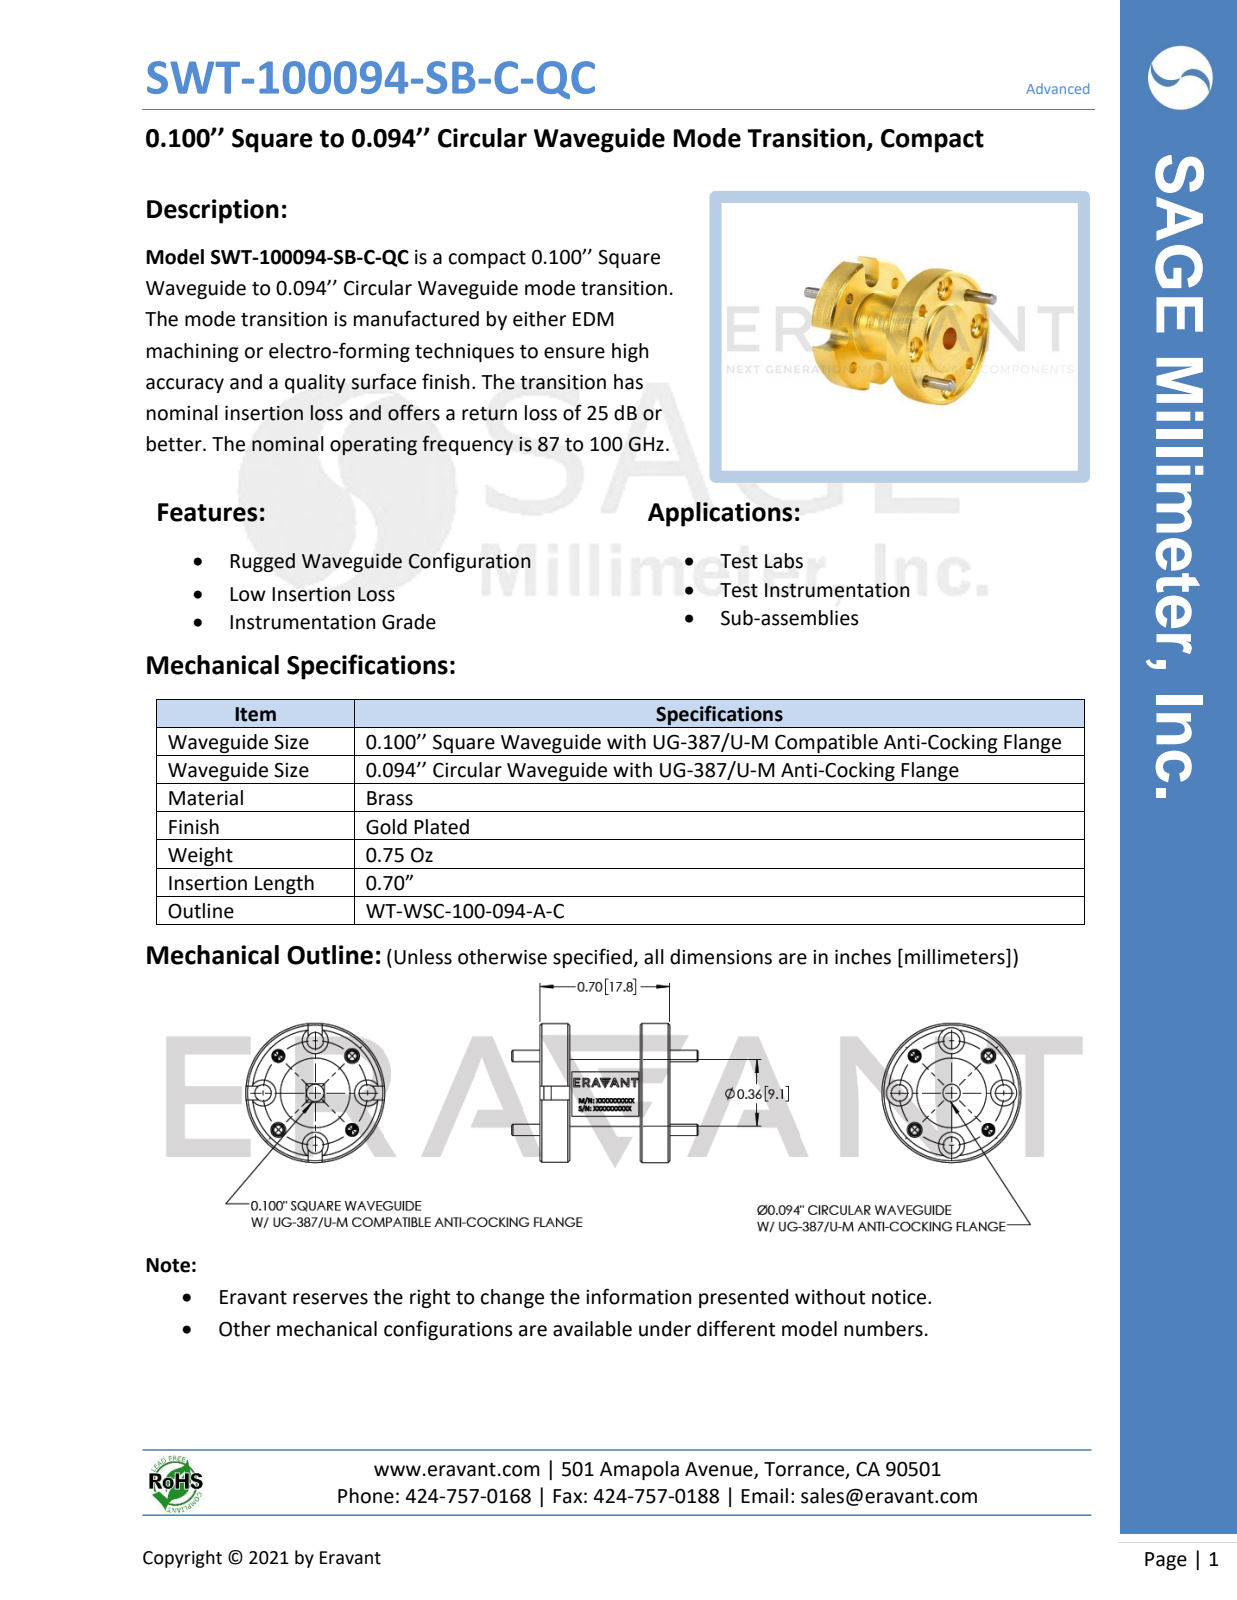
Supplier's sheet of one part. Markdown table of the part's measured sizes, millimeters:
| quantity | value |
| --- | --- |
| part name | WT-WSC-100-094-A-C, Defeatured |
| STEP written by | SolidWorks 2021 (AUTOMOTIVE_DESIGN) |
| units | millimeters |
| bodies | 5 solids, 175 faces (45 planar, 78 cylindrical, 52 other) |
| overall size | 25.5 × 19.1 × 19.1 |
| volume | 2 570 mm³ |
| surface area | 2 223 mm² |
| round holes (diameter × count) | 1.5 × 4, 1.7 × 4, 2.3 × 4, 3.6 × 4, 17.3 × 1 |
| round bosses / shafts (diameter × count) | 1.6 × 4, 19.1 × 1, 9.5 × 1, 9.1 × 1 |
| main face-to-face distances | 3.6, 13.2, 0.5, 4.1, 13.7, 17.3, 9.7, 16.8, 17.8, 1.5 |
| hole center spacings | 5.5, 7.1, 10.1, 13.2, 14.3 |
